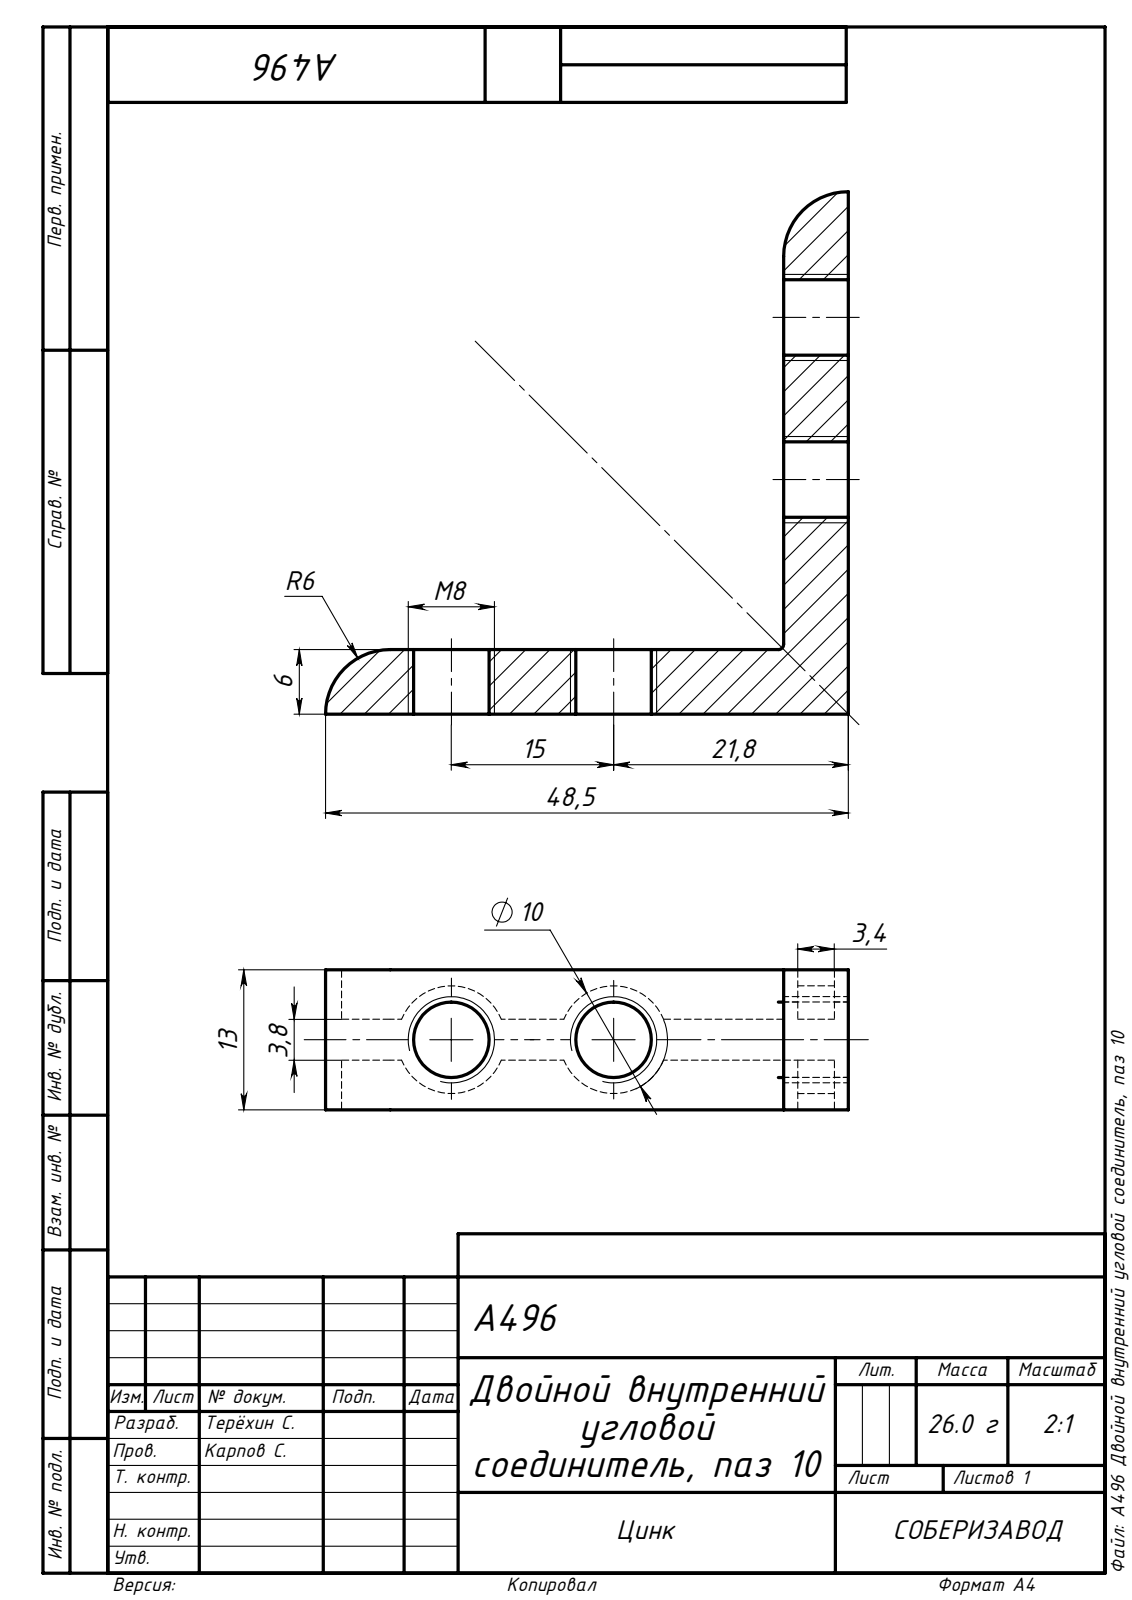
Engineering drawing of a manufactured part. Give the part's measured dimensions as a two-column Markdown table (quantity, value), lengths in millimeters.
| quantity | value |
| --- | --- |
| part name | A496 Двойной внутренний угловой соединитель, паз 10 |
| STEP written by | SolidWorks 2021 (AUTOMOTIVE_DESIGN) |
| units | millimeters |
| bodies | 1 solid, 62 faces (37 planar, 25 cylindrical, 0 other) |
| overall size | 48.5 × 48.5 × 13 |
| volume | 3 874 mm³ |
| surface area | 5 008 mm² |
| round holes (diameter × count) | 7 × 4 |
| partial cylindrical surfaces (radius × count) | 5 × 4, 4.7 × 2, 6 × 2, 0.5 × 1 |
| main face-to-face distances | 1.3, 4.7, 6, 3.4, 4.6, 8.4, 13, 3.8, 3, 10 |
| hole center spacings | 15.06 |
